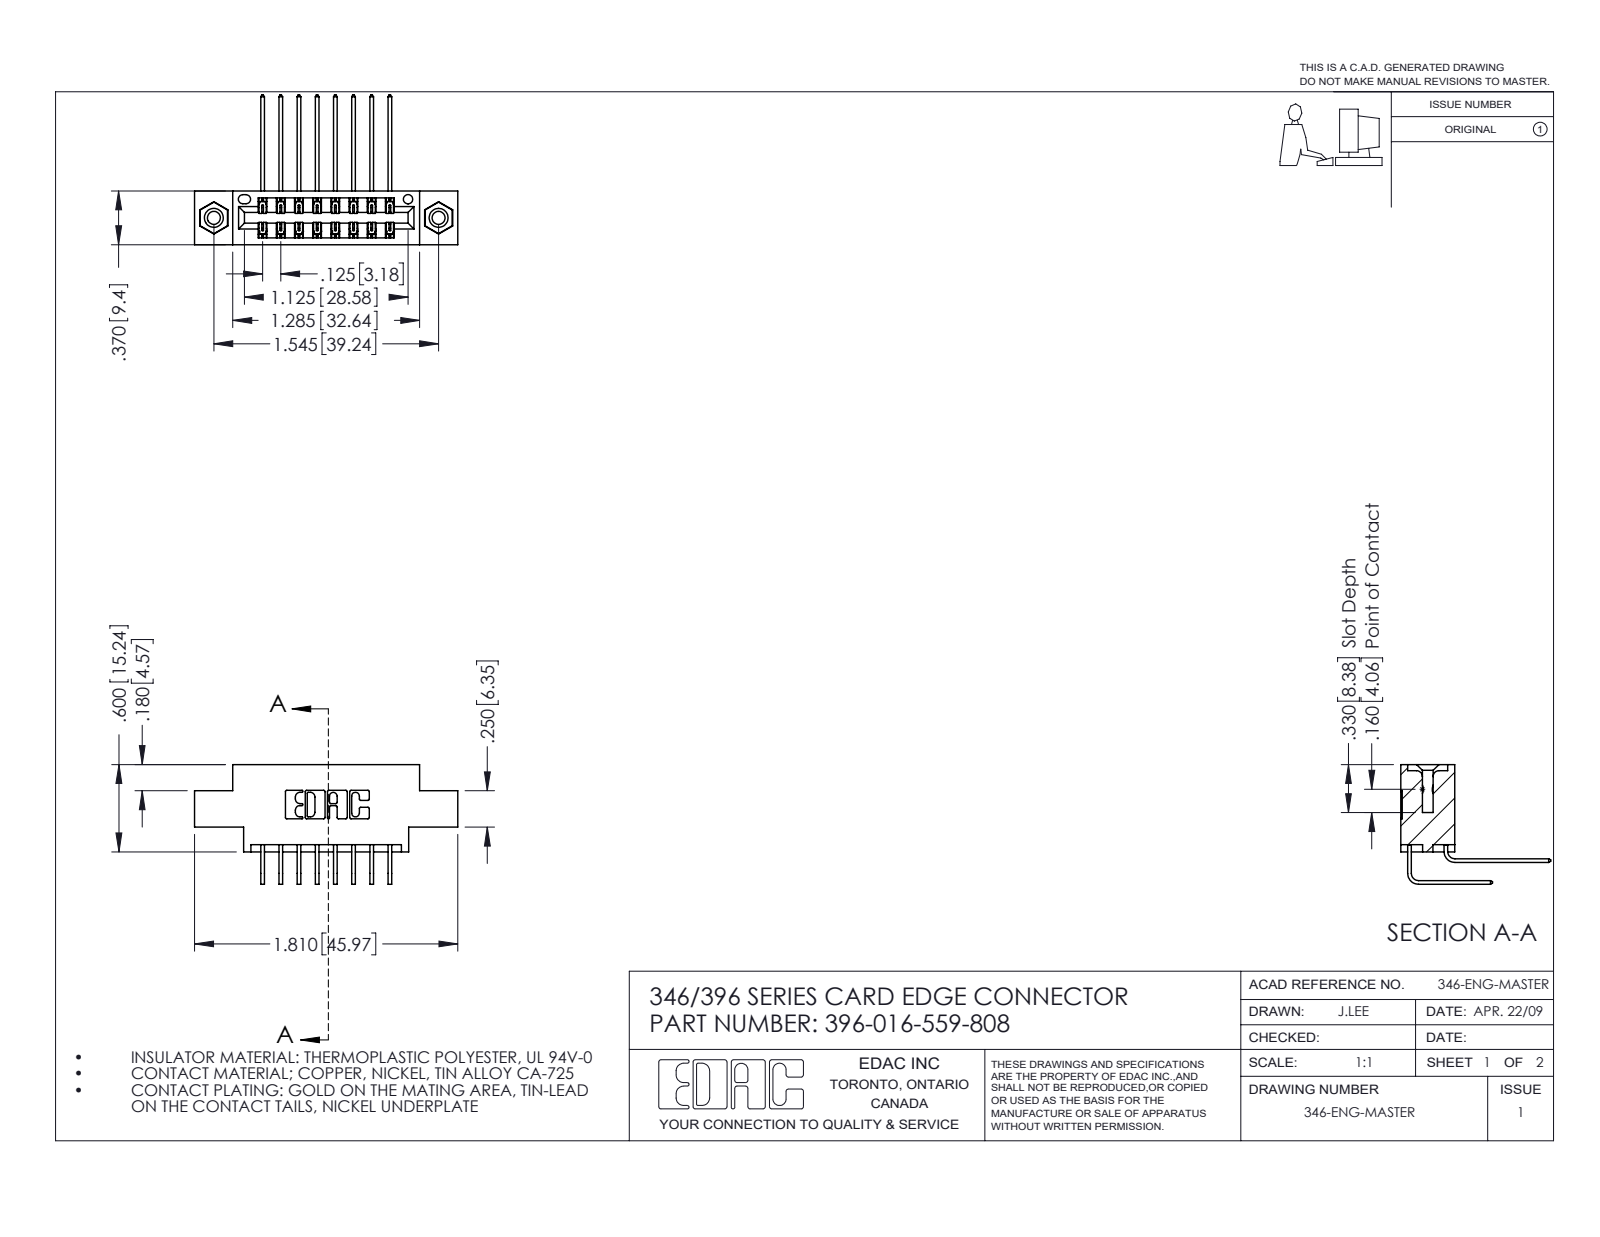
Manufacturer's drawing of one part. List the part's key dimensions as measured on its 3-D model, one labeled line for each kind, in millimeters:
Part name (STEP PRODUCT): 345-250-001_345-250-003-102; 345-292-001_559 Tail - 2; 396-016-559-808; 345-292-001_558 559 Tail - 1 (+1 more)
STEP written by: SolidWorks 2016 (CONFIG_CONTROL_DESIGN)
Units: millimetres
Bodies: 19 solids, 1050 faces (704 planar, 330 cylindrical, 16 other)
Overall size (bounding box): 46 × 26.2 × 20.9
Volume: 4 150 mm³ · Surface area: 5 813 mm²
Round holes (diameter × count): ⌀2.3 ×2, ⌀3.2 ×2, ⌀4 ×2, ⌀1.6 ×1
Round bosses / shafts (diameter × count): ⌀3.9 ×2
Partial cylindrical surfaces — rounded edges, fillets, slot ends (radius × count): R0.2 ×24, R0.3 ×22, R0.2 ×6, R0.8 ×6, R0.7 ×3, R0.4 ×2, R0.6 ×2, R0.6 ×2
Main face-to-face distances: 6.4, 1.2, 9.4, 8.2, 0.6, 1.8, 5.6, 7.6, 3.8, 2.5
Hole centre spacings: 6.2, 34.1, 39.2
